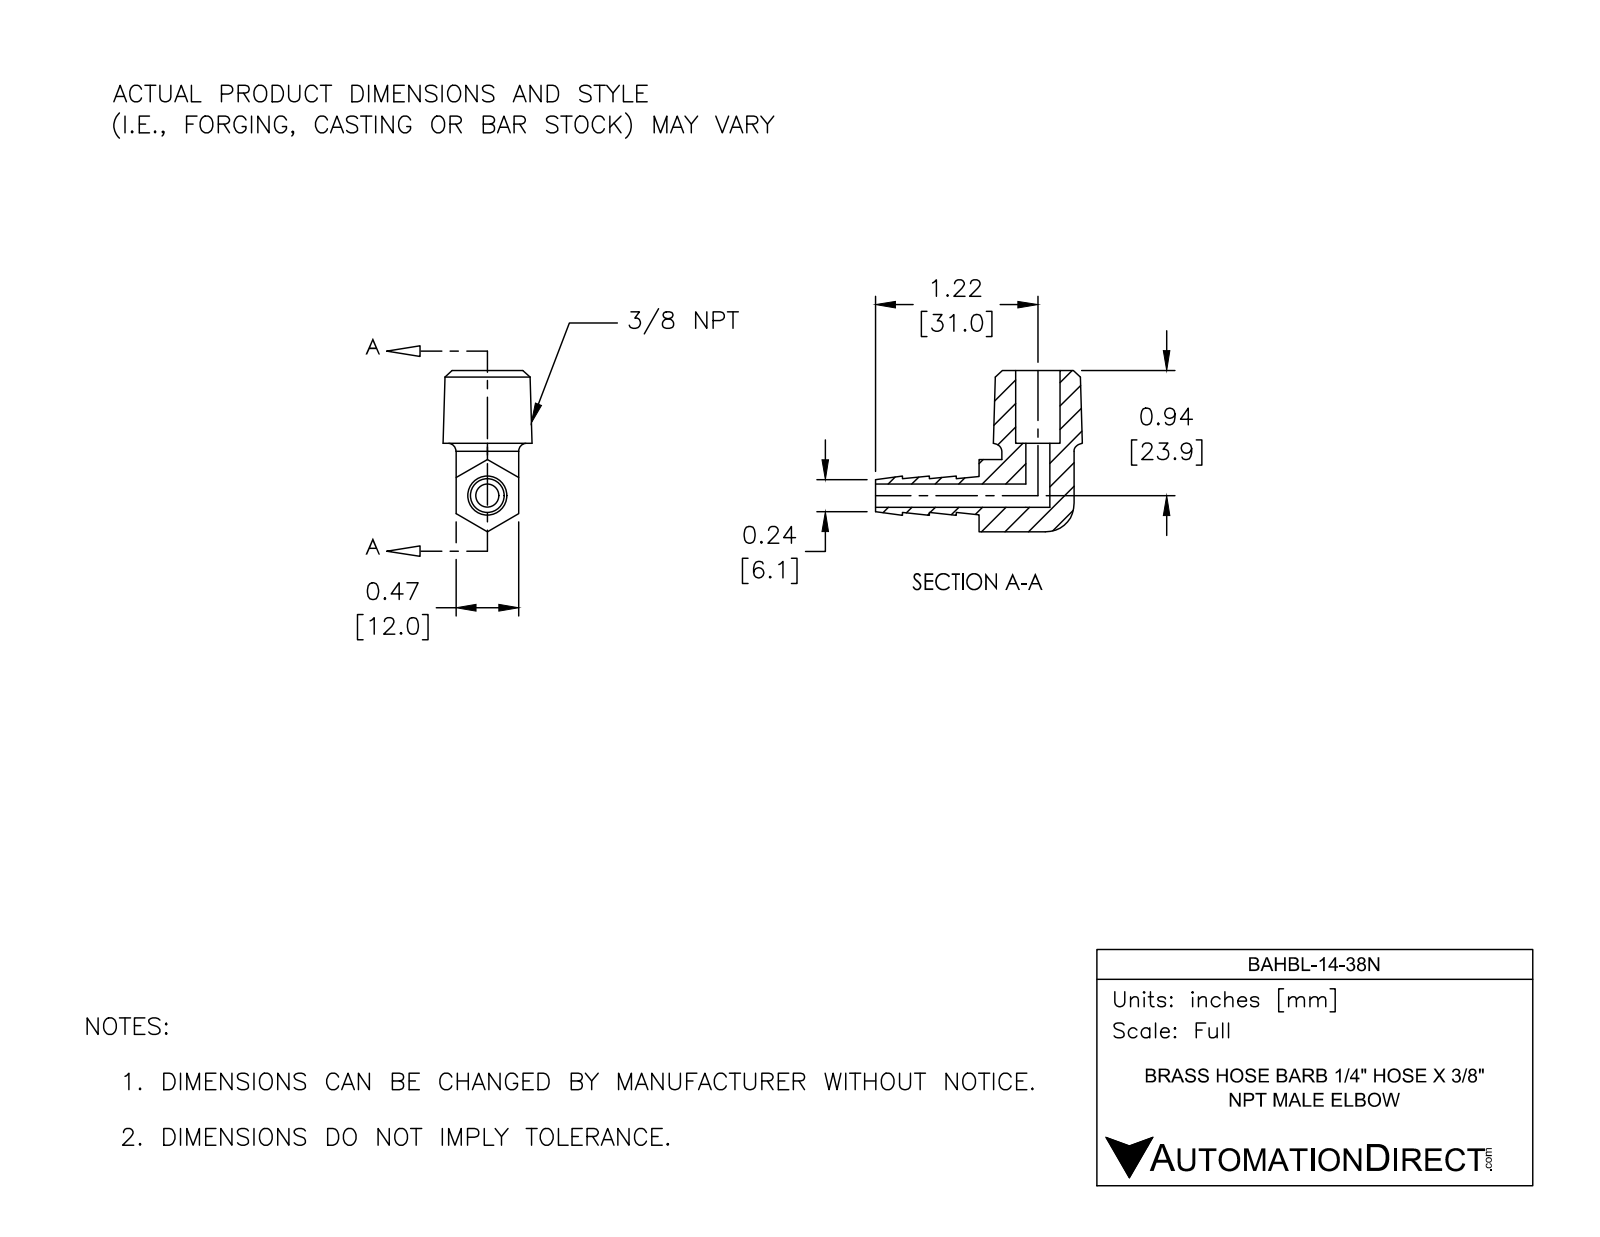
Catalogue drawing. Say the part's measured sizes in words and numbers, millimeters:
The part is named "BAHBL-14-38N". Its 3-D file was written by "SolidWorks 2017 (AUTOMOTIVE_DESIGN)". It is 1 solid with 50 faces: 24 planar, 14 cylindrical and 12 other. Overall it measures 39.5 by 30.8 by 17 millimeters. Its volume is 4 850 cubic millimeters and its surface area 3 321 square millimeters. Round holes: 1 of diameter 4.4, 1 of diameter 4.6, 1 of diameter 8.5. Partial cylindrical surfaces (rounded edges, fillets, slot ends): 6 of radius 1.5, 2 of radius 6.4. The main face-to-face distances are 12, 13.9, 5.2, 10.3, 19.8, 12.2, 26.1, 4.3, 9.5, 14.6.
